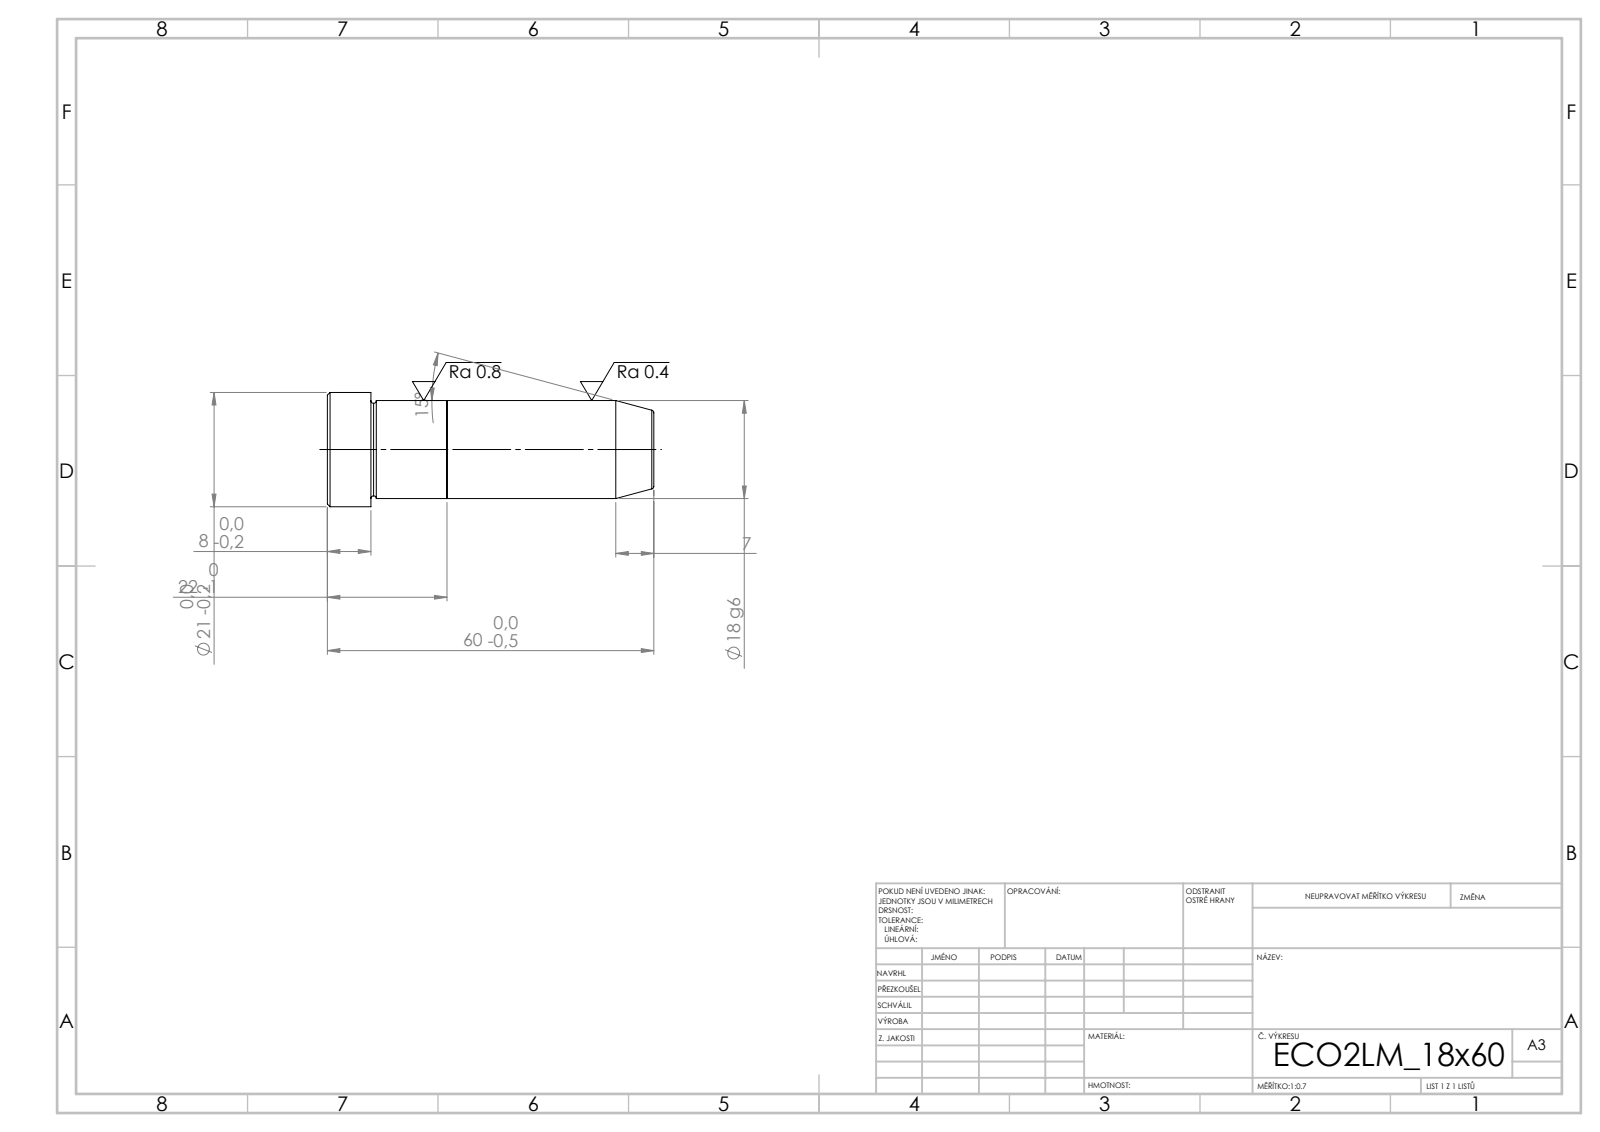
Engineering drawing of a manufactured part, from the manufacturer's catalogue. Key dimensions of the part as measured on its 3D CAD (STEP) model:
STEP written by: SolidWorks 2019 (CONFIG_CONTROL_DESIGN)
Units: millimetres
Bodies: 2 solids, 21 faces (5 planar, 6 cylindrical, 10 other)
Overall size (bounding box): 60 × 21 × 21
Volume: 15 627 mm³ · Surface area: 4 551 mm²
Round bosses / shafts (diameter × count): ⌀21 ×1, ⌀18 ×1
Main face-to-face distances: 22, 38, 60, 52, 14, 8
